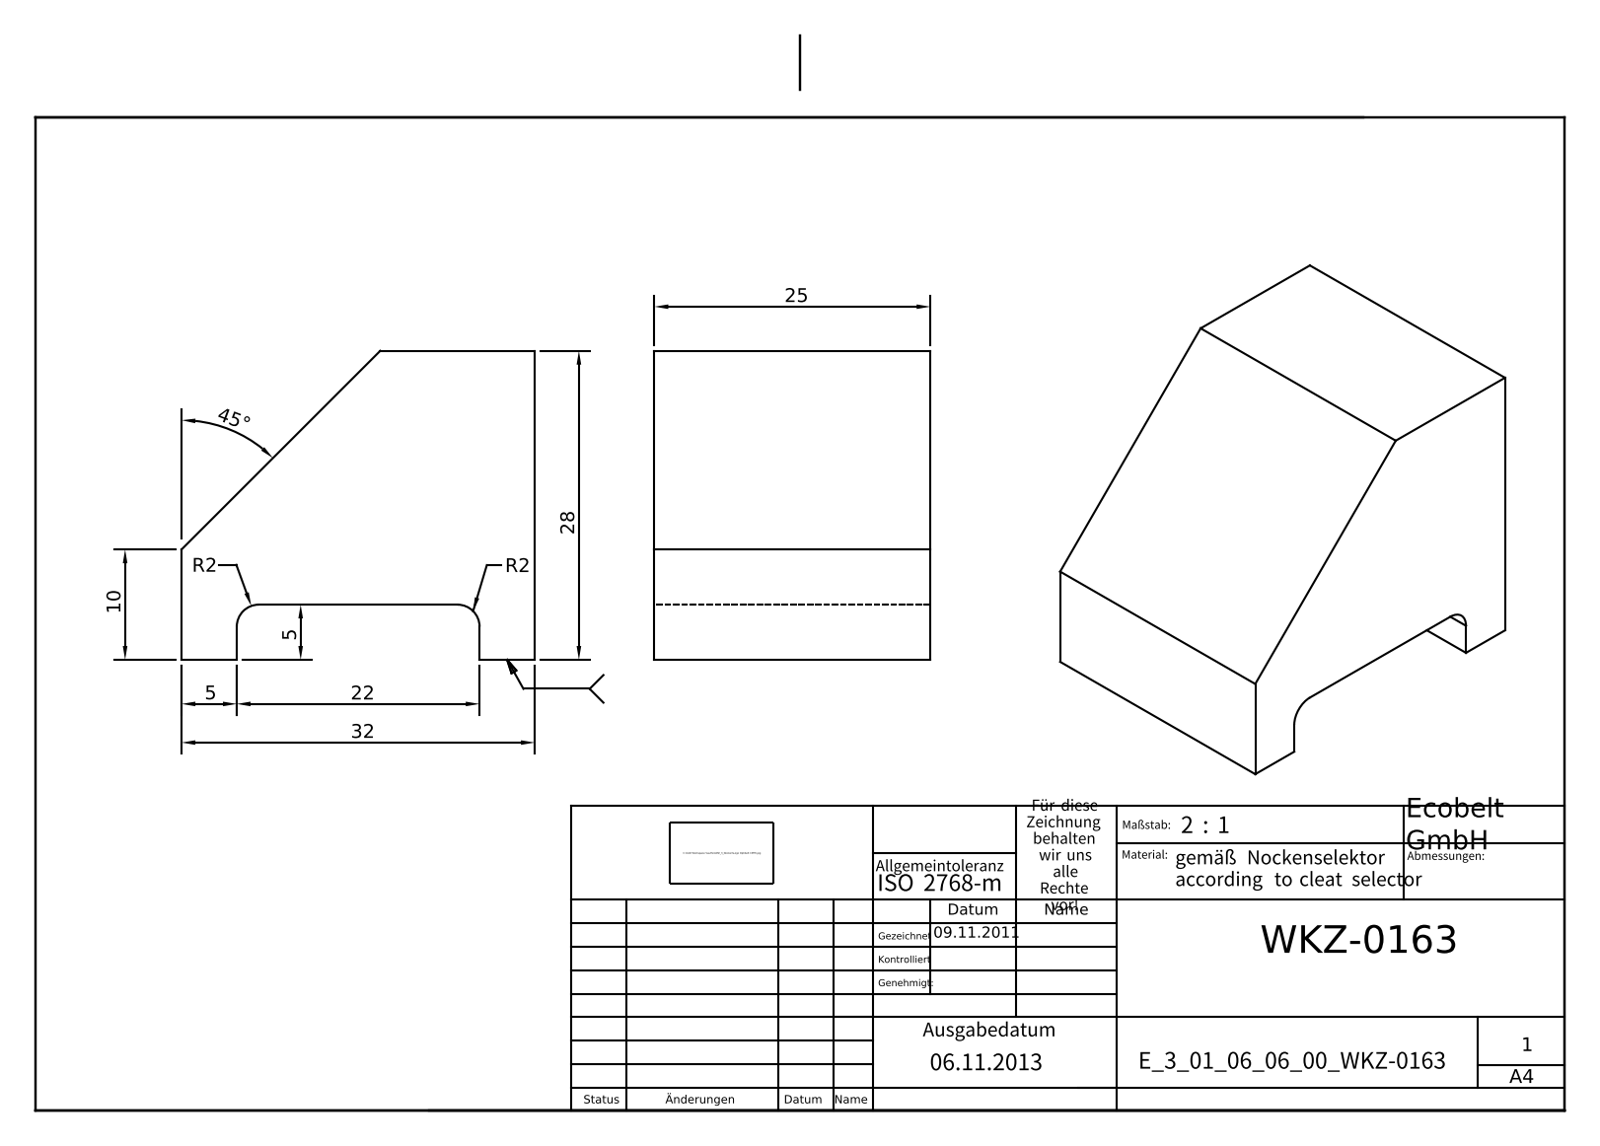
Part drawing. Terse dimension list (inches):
name: E_3_01_06_06_00_WKZ-0163
written by: Autodesk Inventor 2025 (AUTOMOTIVE_DESIGN)
unit: in
bodies: 1 solid, 13 faces (11 planar, 2 cylindrical, 0 other)
size: 1.26 × 1.102 × 0.984
volume: 0.955 in³; area: 6.502 in²
rounds: 2× R0.079
face distances: 0.984, 0.197, 0.906, 1.26, 1.102, 1.063, 0.866
